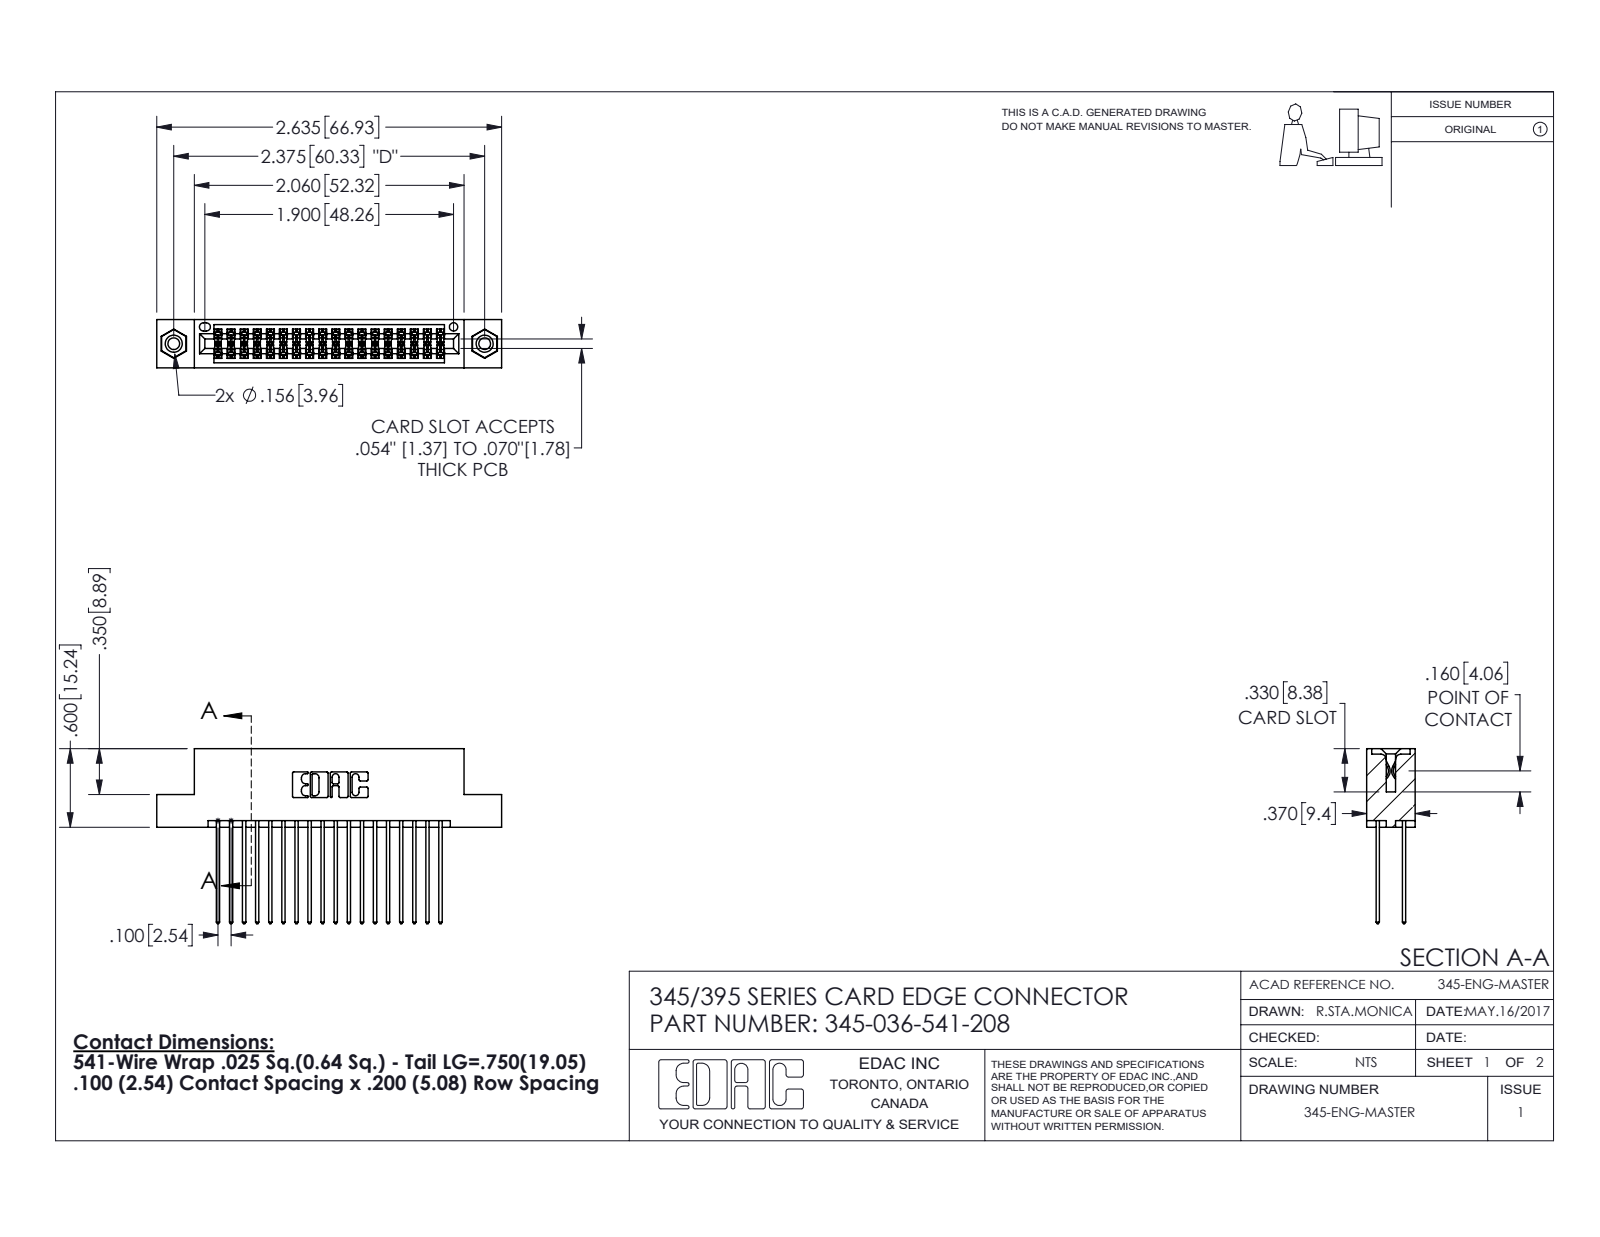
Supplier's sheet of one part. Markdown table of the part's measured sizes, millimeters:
| quantity | value |
| --- | --- |
| part name | 345-036-541-208; 345 Part_Flush Mounting Lugs - 0.156 Dia-TI; 345-292-001_345-293-141; 345-250-001_345-250-003-102 |
| STEP written by | SolidWorks 2016 (CONFIG_CONTROL_DESIGN) |
| units | millimeters |
| bodies | 39 solids, 1986 faces (1300 planar, 670 cylindrical, 16 other) |
| overall size | 66.9 × 34 × 9.4 |
| volume | 6 470 mm³ |
| surface area | 10 100 mm² |
| round holes (diameter × count) | 2.3 × 2, 3.2 × 2, 4 × 2, 1.6 × 1 |
| round bosses / shafts (diameter × count) | 3.9 × 2 |
| partial cylindrical surfaces (radius × count) | 0.2 × 54, 0.3 × 36, 0.3 × 22, 0.2 × 6, 0.8 × 6, 0.7 × 3, 0.4 × 2, 0.5 × 2 |
| main face-to-face distances | 1.8, 7.6, 5.1, 2.5, 6.9, 0.6, 9.4, 5.7, 4.4, 2.5 |
| hole center spacings | 6.9, 54.4, 60.3 |
